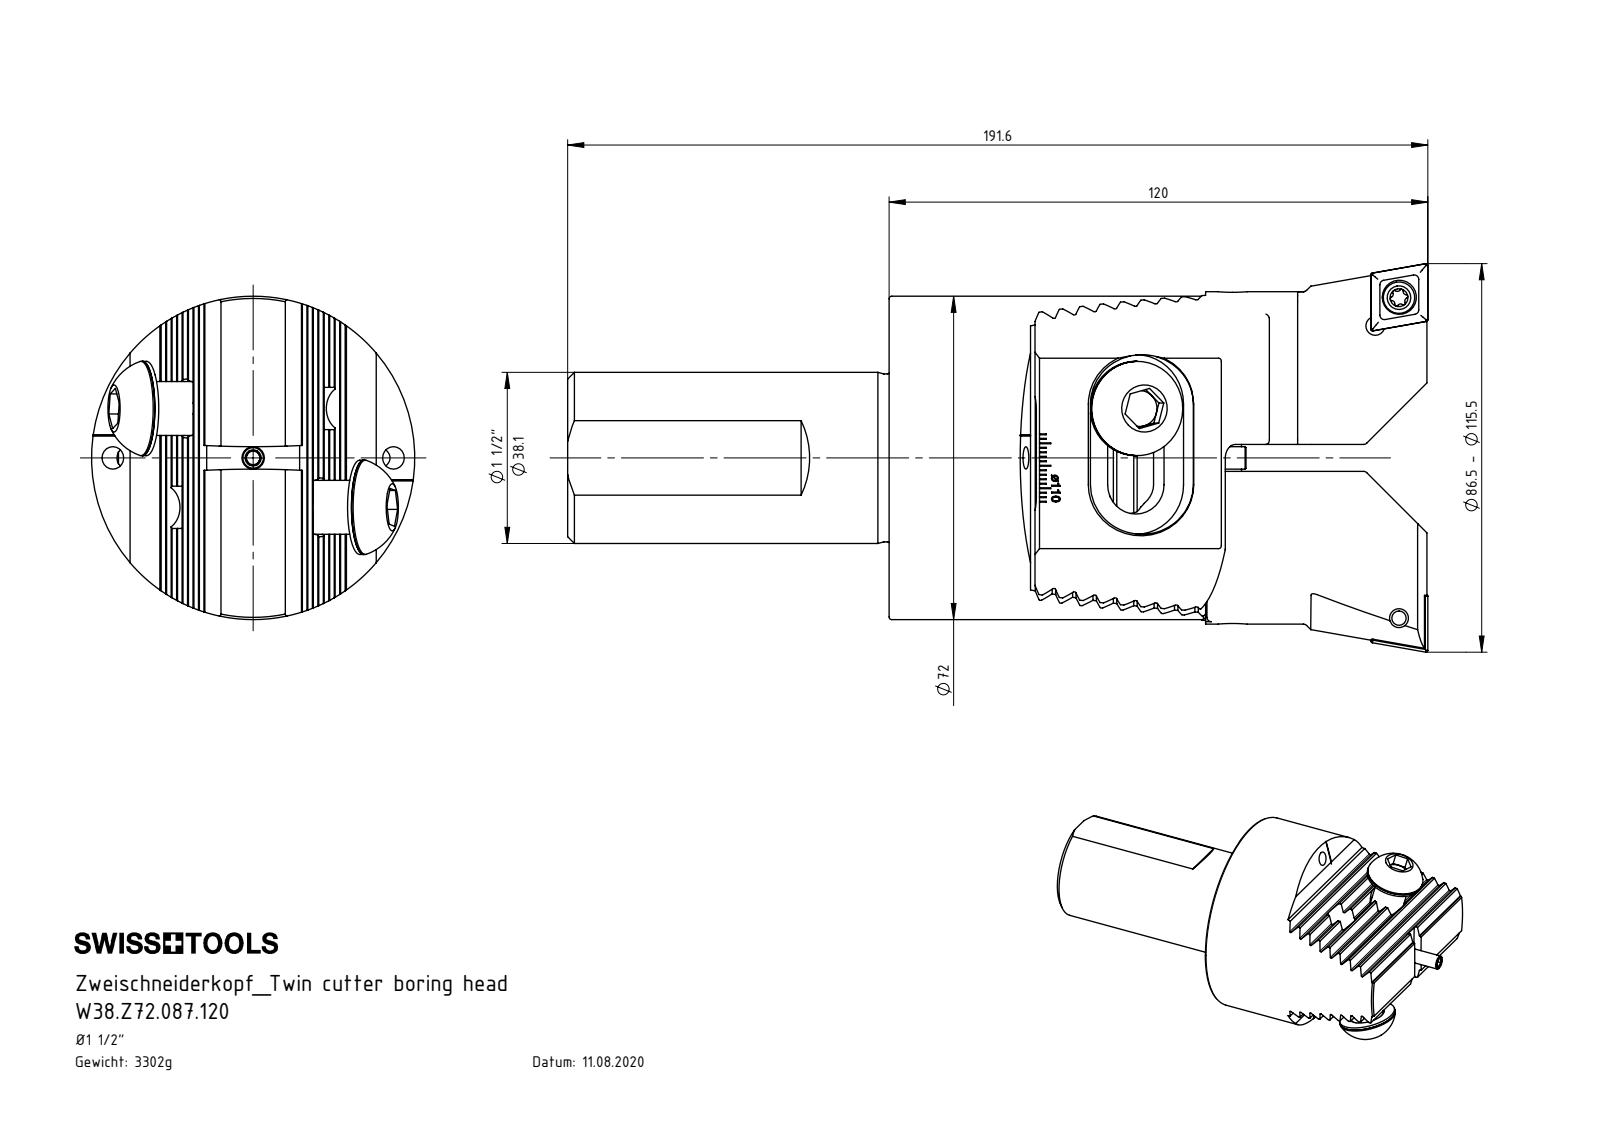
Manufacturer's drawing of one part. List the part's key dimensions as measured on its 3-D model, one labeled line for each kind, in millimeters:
Part name (STEP PRODUCT): Z72-ER3.001.030; Z72-ER1.001.025; W38.Z72.087.120; Z72-ER1.002.025_A (+6 more)
STEP written by: SolidWorks 2022 (CONFIG_CONTROL_DESIGN)
Units: millimetres
Bodies: 13 solids, 995 faces (528 planar, 222 cylindrical, 245 other)
Overall size (bounding box): 191.6 × 86.5 × 72
Volume: 421 629 mm³ · Surface area: 81 779 mm²
Round holes (diameter × count): ⌀4.2 ×4, ⌀5 ×4, ⌀13.5 ×3, ⌀2 ×2, ⌀5.5 ×2, ⌀7.6 ×2, ⌀10.25 ×2, ⌀13 ×2, ⌀3.3 ×1, ⌀10.7 ×1
Round bosses / shafts (diameter × count): ⌀21 ×4, ⌀12 ×2, ⌀7 ×2, ⌀5 ×2, ⌀72 ×1, ⌀38.1 ×1, ⌀37.4 ×1, ⌀6 ×1
Partial cylindrical surfaces — rounded edges, fillets, slot ends (radius × count): R0.34 ×18, R0.34 ×16, R1 ×16, R0.39 ×12, R0.69 ×12, R3 ×6, R6.5 ×4, R11 ×4
Main face-to-face distances: 4.07, 8.14, 12.21, 16.28, 20.35, 24.42, 4.01, 28.49, 4.13, 4.11
Hole centre spacings: 8.21, 8.33, 20, 65.26, 65.36, 71.43, 97.34, 104.36
